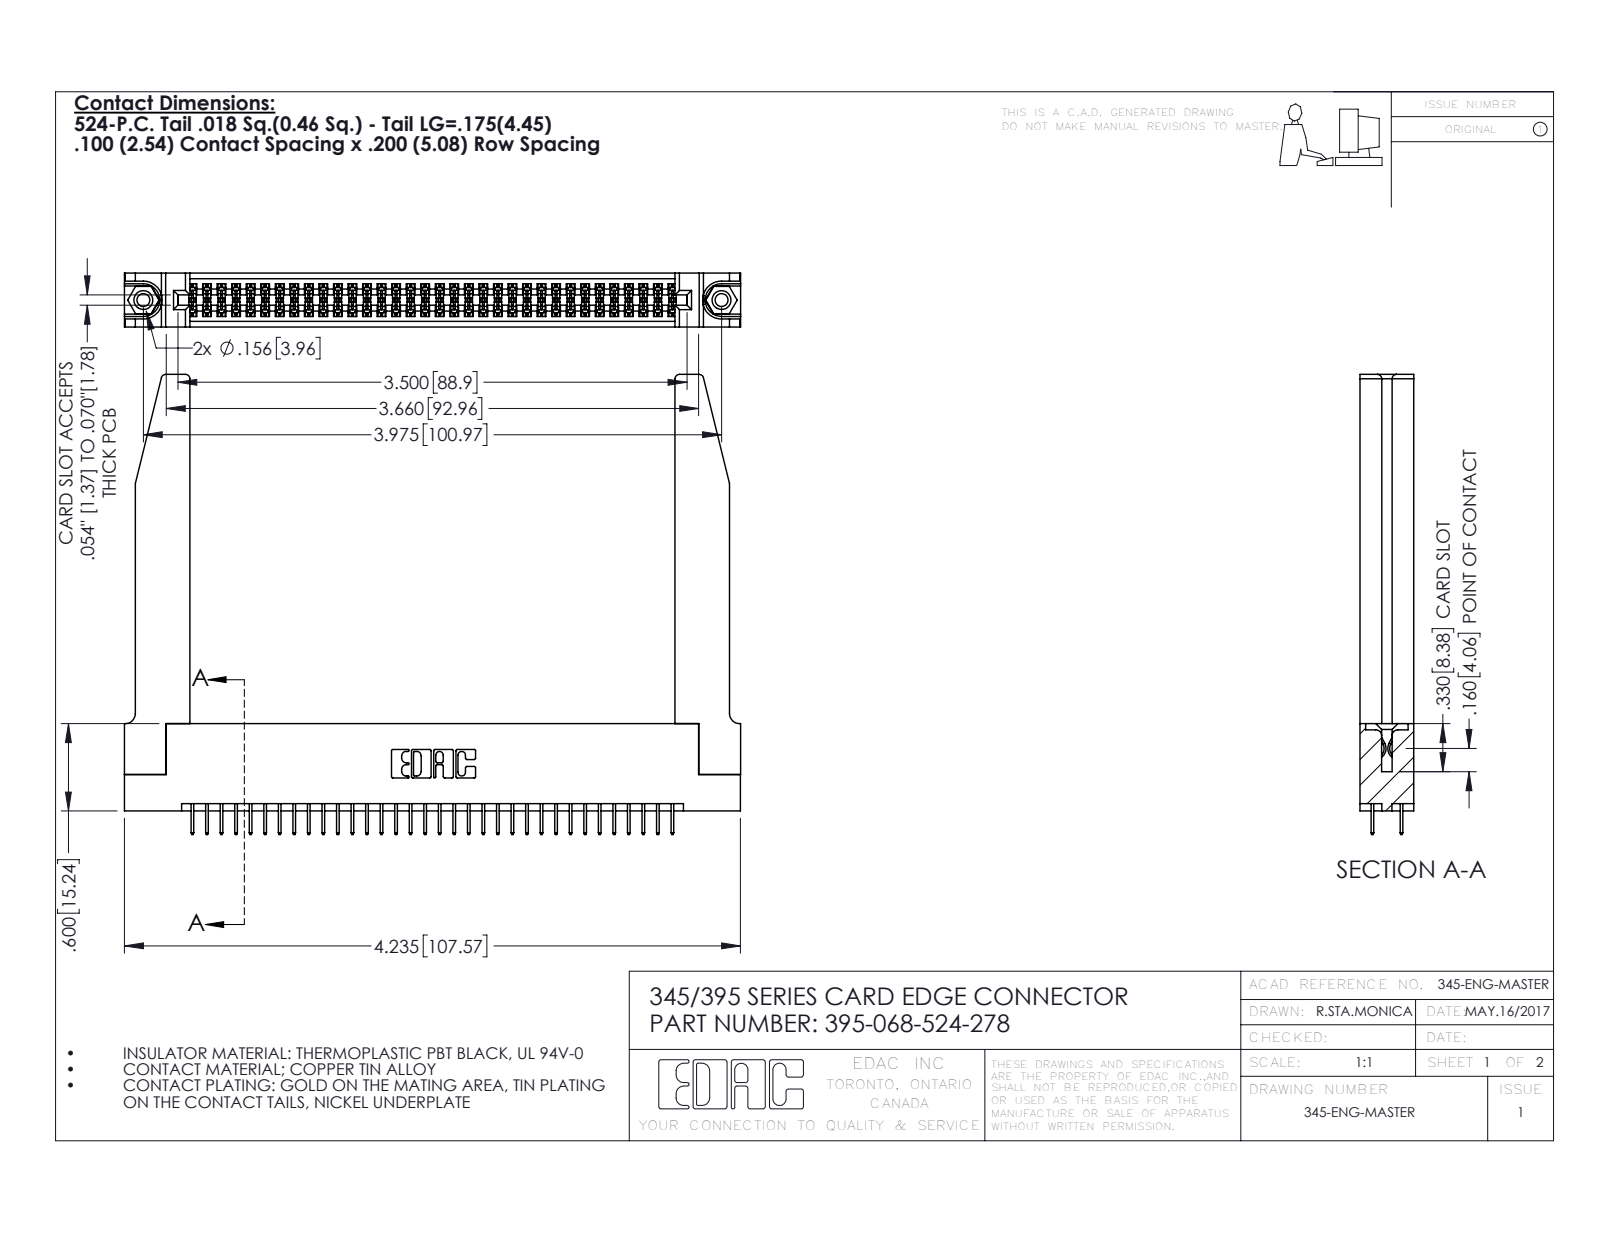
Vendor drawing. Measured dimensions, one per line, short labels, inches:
name: 345 Part_Flush Mounting Lugs - 0.156 Dia-TH; 395-068-524-278; 345-220-078_345-220-078; 345-292-001_345-293-124 (+1 more)
written by: SolidWorks 2016 (CONFIG_CONTROL_DESIGN)
unit: in
bodies: 73 solids, 4032 faces (2874 planar, 1106 cylindrical, 52 other)
size: 4.236 × 3.162 × 0.37
volume: 1.101 in³; area: 33.48 in²
holes: 2× ⌀0.089, 2× ⌀0.125, 2× ⌀0.156, 1× ⌀0.064
bosses: 2× ⌀0.155
rounds: 102× R0.006, 22× R0.01, 8× R0.03, 6× R0.007, 6× R0.031, 3× R0.026, 2× R0.014, 2× R0.019
face distances: 0.37, 0.072, 0.298, 0.2, 0.098, 0.272, 0.025, 0.225, 0.15, 0.148
hole spacings: 0.27, 3.74, 3.975
